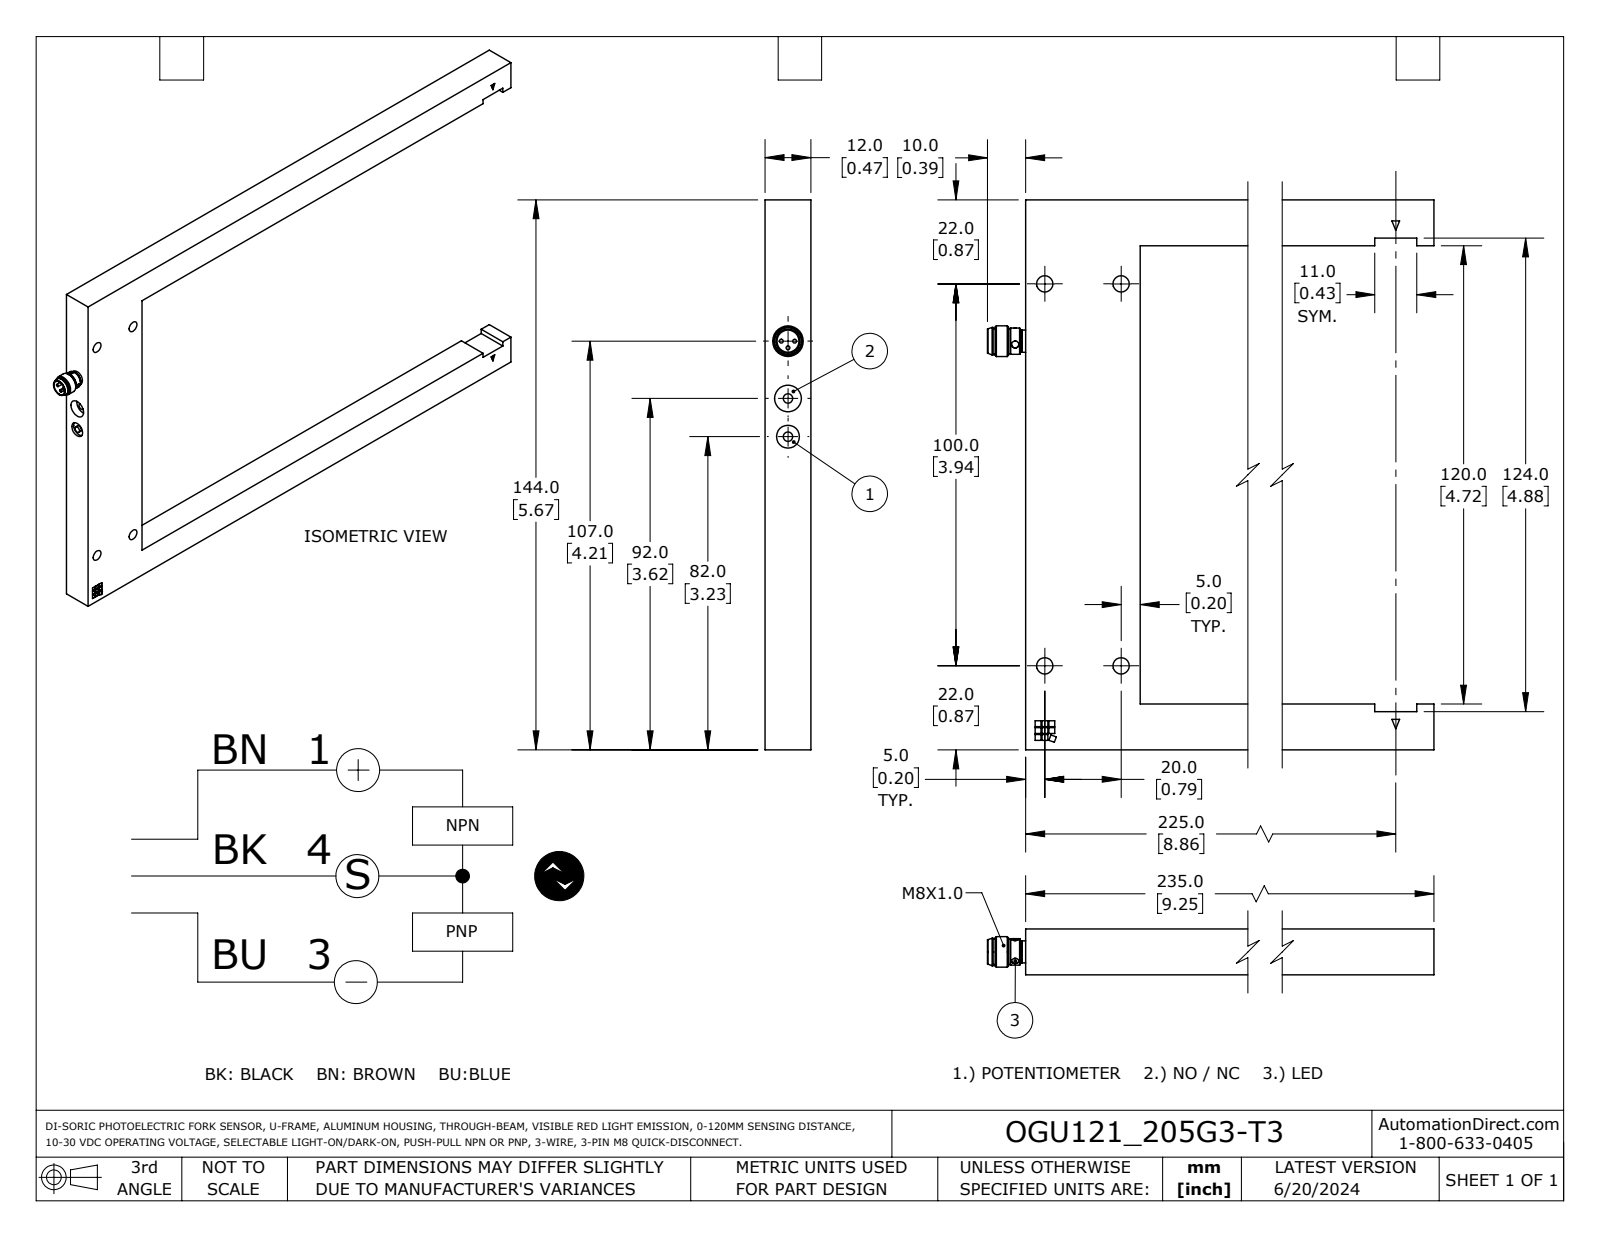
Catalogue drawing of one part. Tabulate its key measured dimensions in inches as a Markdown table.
| quantity | value |
| --- | --- |
| part name | OGU121205G3-T3 |
| STEP written by | SolidWorks 2023 (AUTOMOTIVE_DESIGN) |
| units | inches |
| bodies | 1 solid, 183 faces (137 planar, 41 cylindrical, 5 other) |
| overall size | 9.646 × 5.669 × 0.472 |
| volume | 6.698 in³ |
| surface area | 52.08 in² |
| round holes (diameter × count) | 0.169 × 4, 0.075 × 3, 0.079 × 1, 0.236 × 1, 0.276 × 1 |
| round bosses / shafts (diameter × count) | 0.039 × 3, 0.098 × 2, 0.315 × 1, 0.283 × 1, 0.272 × 1, 0.26 × 1, 0.252 × 1, 0.228 × 1 |
| main face-to-face distances | 0.472, 5.197, 5.669, 4.724, 1.181, 9.252, 8.071, 0.079, 0.394, 5.276 |
| hole center spacings | 0.787, 3.937, 4.015, 0.394, 0.591, 0.984 |
